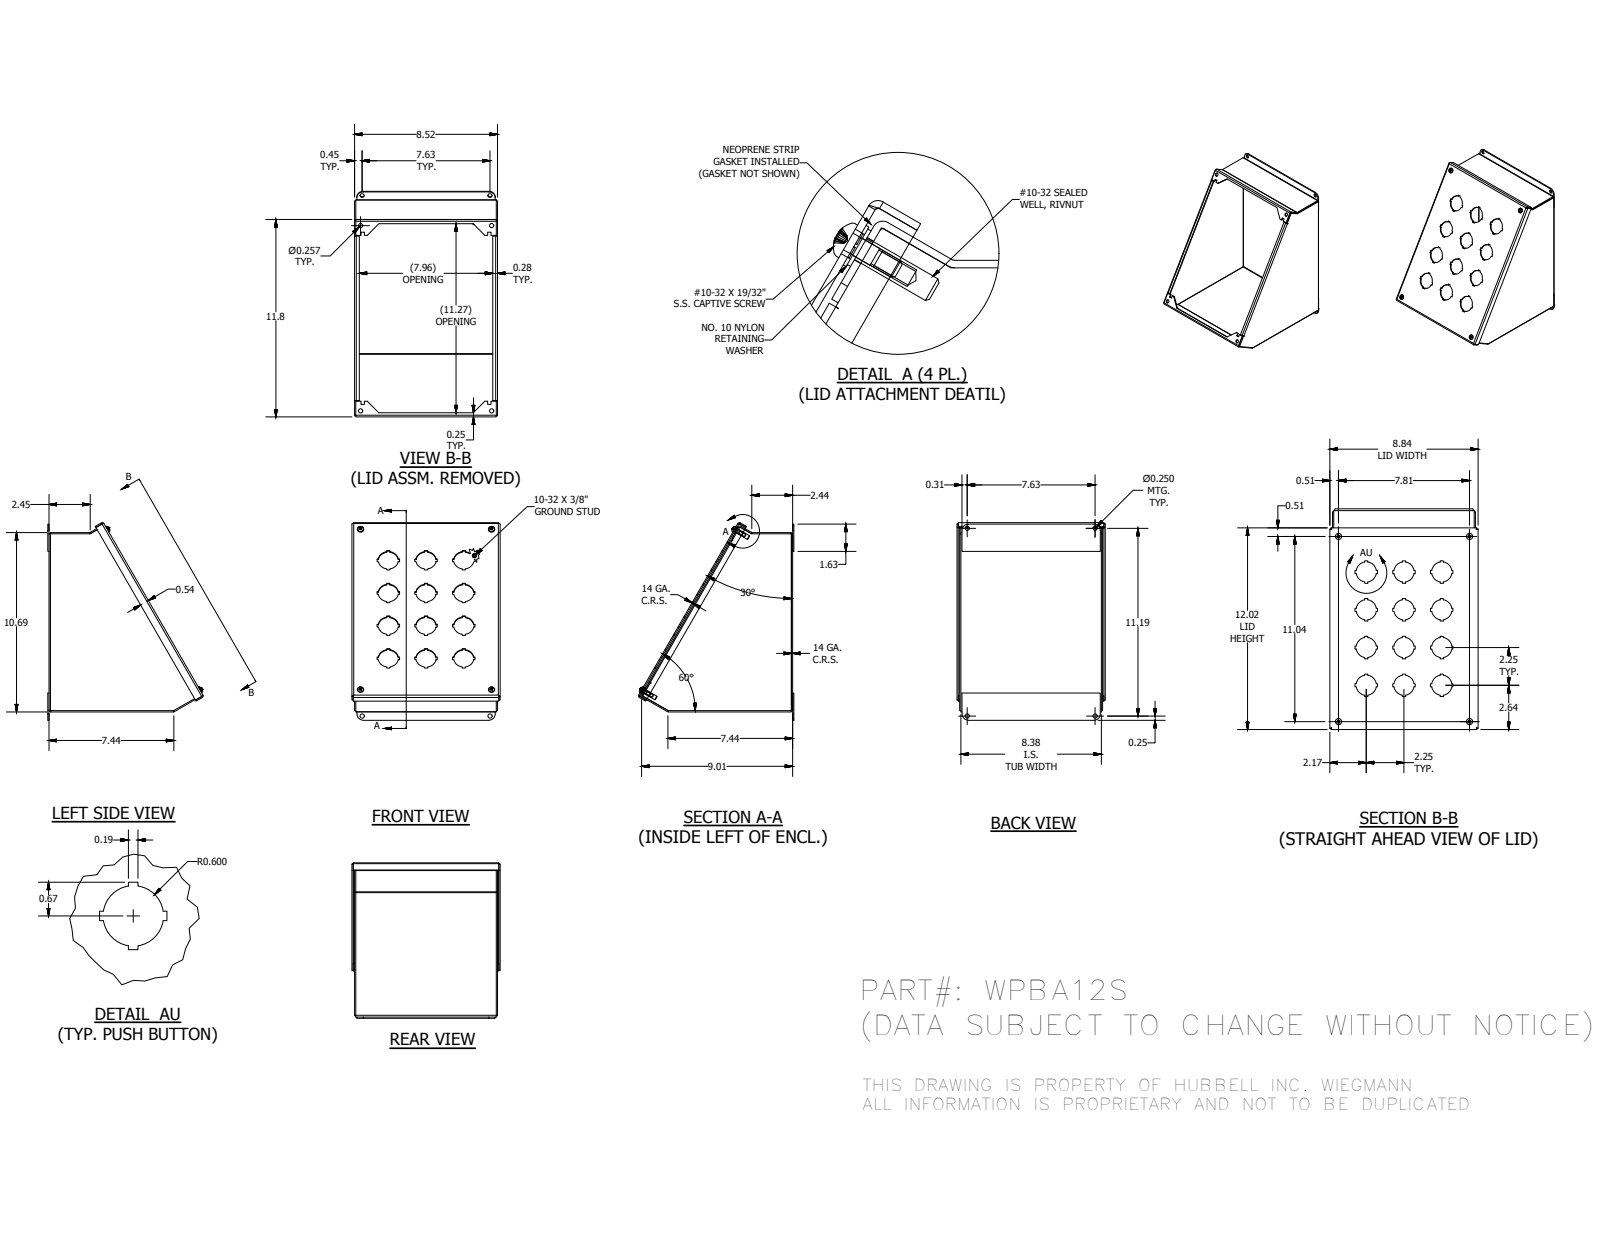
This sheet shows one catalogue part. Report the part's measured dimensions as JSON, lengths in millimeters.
{"part_name": "WPBA12SBKP; WPBA4ROWEWPR; WPBA4ROWEWPL; 34984 (+6 more)", "step_written_by": "Autodesk Inventor 2014 (AUTOMOTIVE_DESIGN)", "units": "millimeters", "bodies": {"solids": 19, "faces": 672, "planar": 435, "cylindrical": 138, "other": 99}, "overall_size": [299.29, 235.35, 224.46], "volume_mm3": 575551, "surface_area_mm2": 627793, "round_holes": [[30.48, 12], [3.96, 4], [4.98, 4], [6.35, 4], [6.53, 4], [7.06, 4], [7.14, 4]], "round_bosses_or_shafts": [[4.83, 5], [11.51, 4], [10.31, 4], [9.47, 4], [6.3, 4], [6.35, 1]], "partial_cylinders_radius": [[0.79, 12], [2.67, 12], [2.27, 4], [9.53, 4]], "face_to_face_distances": [1.88, 214.6, 212.72, 216.48, 269.65, 3.76, 267.77, 271.53, 296.9, 3.65], "hole_center_spacings": [127.79, 57.15, 80.82, 114.3, 68.42, 80.83, 112.93, 148.96]}
